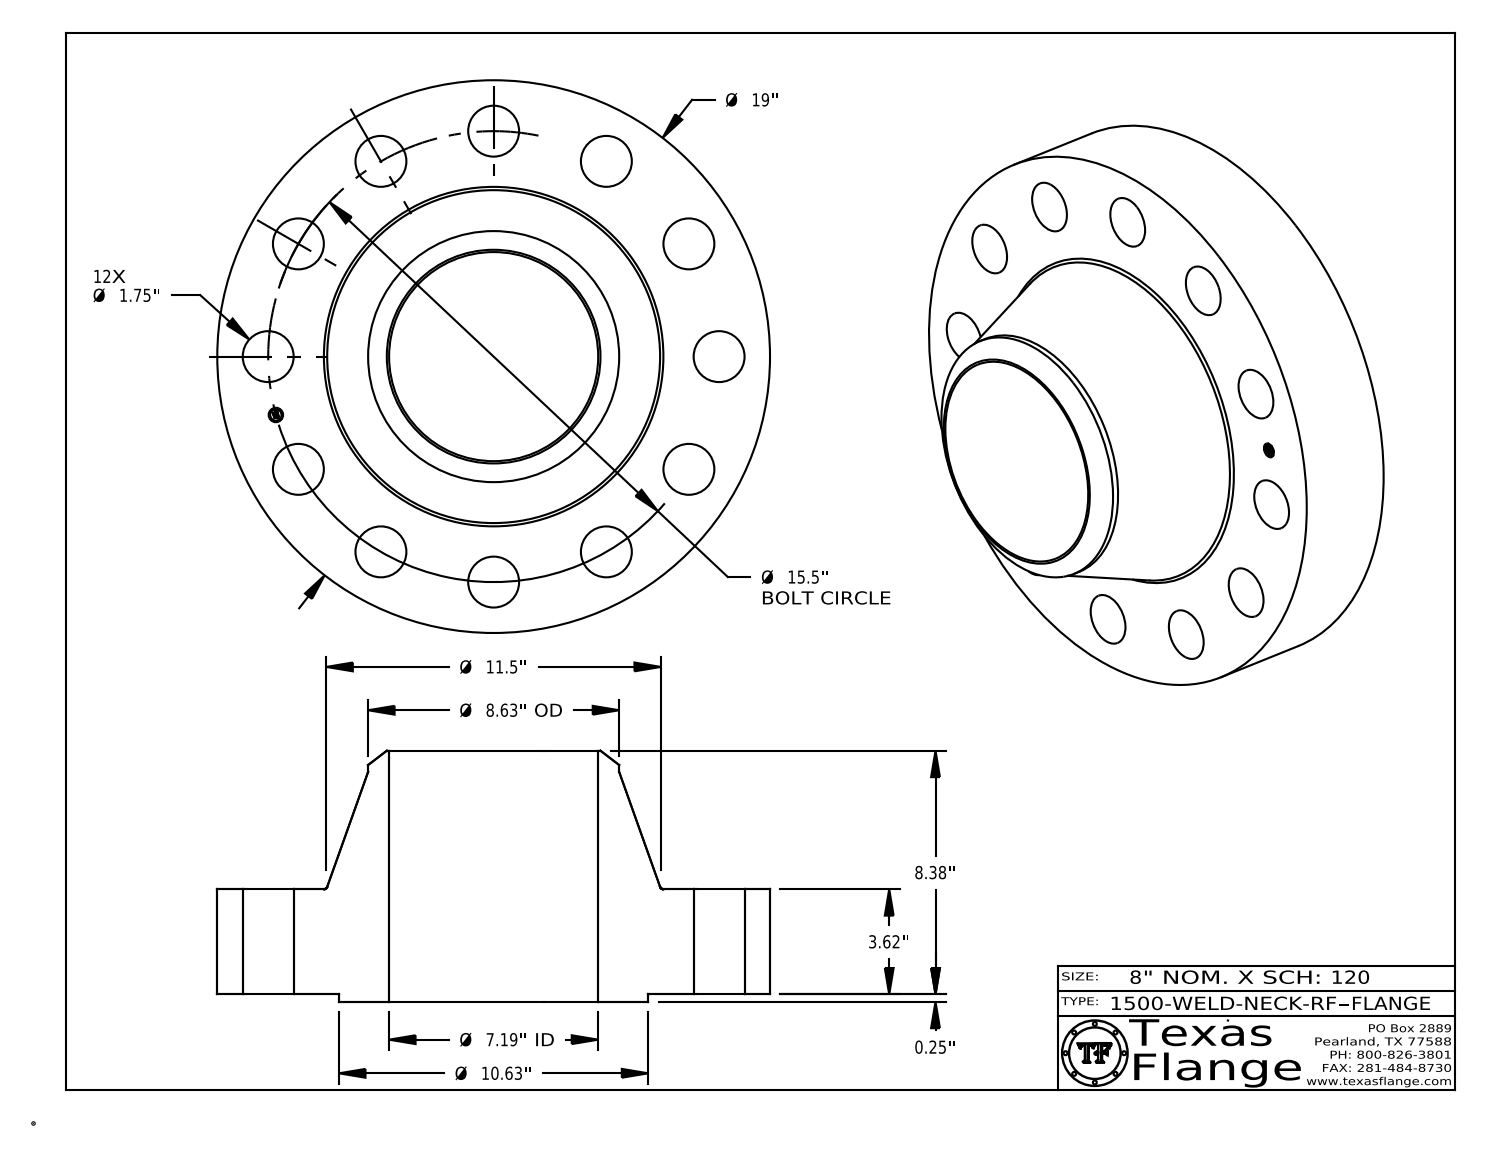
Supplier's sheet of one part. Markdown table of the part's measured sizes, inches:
| quantity | value |
| --- | --- |
| part name | 1500-WELD-NECK-RF |
| STEP written by | CATIA V5 STEP AP214 (AUTOMOTIVE_DESIGN) |
| units | inches |
| bodies | 1 solid, 427 faces (369 planar, 52 cylindrical, 6 other) |
| overall size | 19 × 19 × 8.63 |
| volume | 955.5 in³ |
| surface area | 1 186 in² |
| round holes (diameter × count) | 1.75 × 12, 0.495 × 1, 7.187 × 1 |
| round bosses / shafts (diameter × count) | 0.03 × 8, 19 × 1, 10.63 × 1, 8.63 × 1, 0.39 × 1 |
| main face-to-face distances | 3.62, 0.25, 3.87, 8.63, 8.38, 4.76, 0.015, 3.855, 3.605, 4.775 |
| hole center spacings | 7.75, 7.75, 13.424, 4.012, 10.961, 14.972, 4.011, 10.96 |
